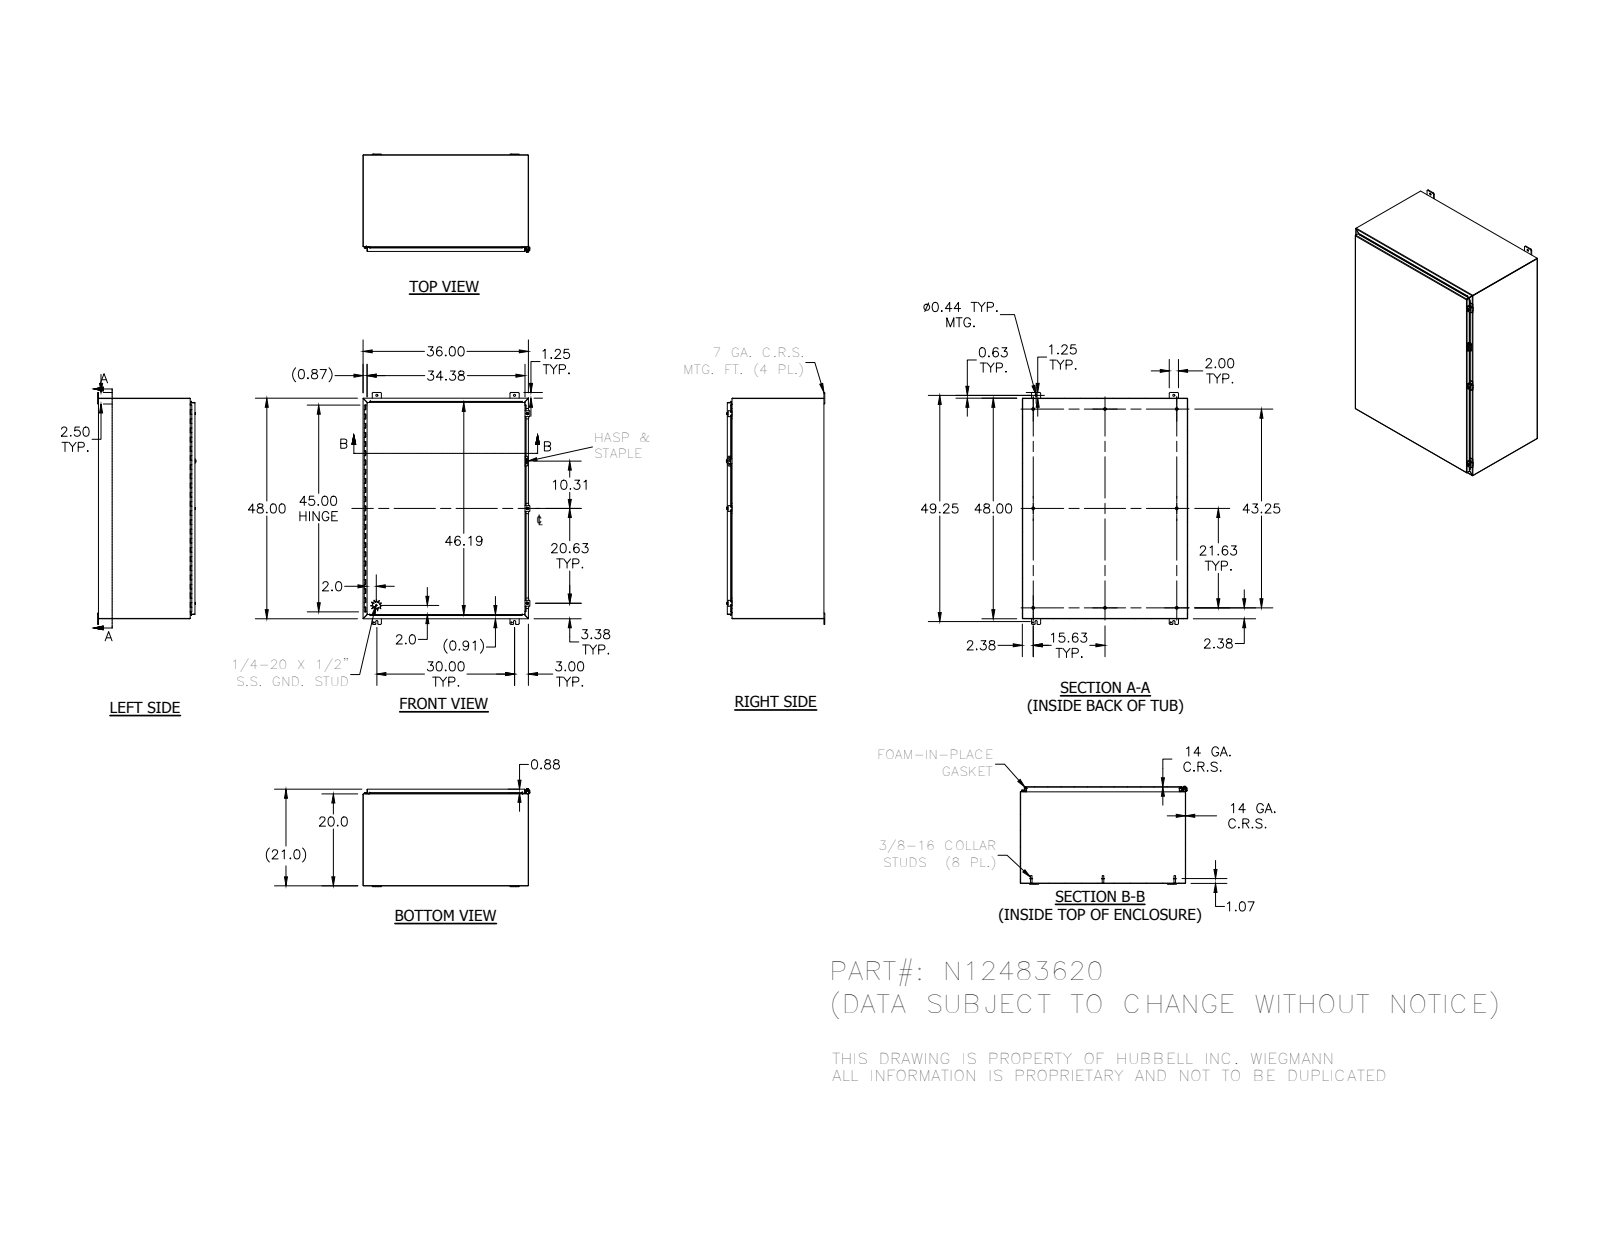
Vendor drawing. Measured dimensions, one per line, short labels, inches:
name: N12483620; 34840; 38413; N123620TB (+8 more)
written by: Autodesk Inventor 2012 (AUTOMOTIVE_DESIGN)
unit: in
bodies: 38 solids, 1249 faces (734 planar, 392 cylindrical, 123 other)
size: 50.5 × 36.311 × 21.41
volume: 559 in³; area: 14 877 in²
holes: 4× ⌀0.313, 4× ⌀0.438, 3× ⌀0.11, 3× ⌀0.211, 3× ⌀0.281, 3× ⌀0.3, 1× ⌀0.125, 1× ⌀0.156, 1× ⌀0.5
bosses: 8× ⌀0.625, 8× ⌀0.33, 5× ⌀0.25, 3× ⌀0.52, 3× ⌀0.5, 3× ⌀0.35, 1× ⌀0.337, 1× ⌀0.12
rounds: 39× R0.03, 27× R0.125, 27× R0.25, 21× R0.031, 21× R0.105, 15× R0.063, 6× R0.1, 6× R0.141
face distances: 0.074, 20.959, 35.926, 20.885, 21.033, 47.926, 35.852, 36, 47.852, 48
hole spacings: 1.593, 30, 48, 56.604, 0.791, 10.327, 29.348, 30.72
